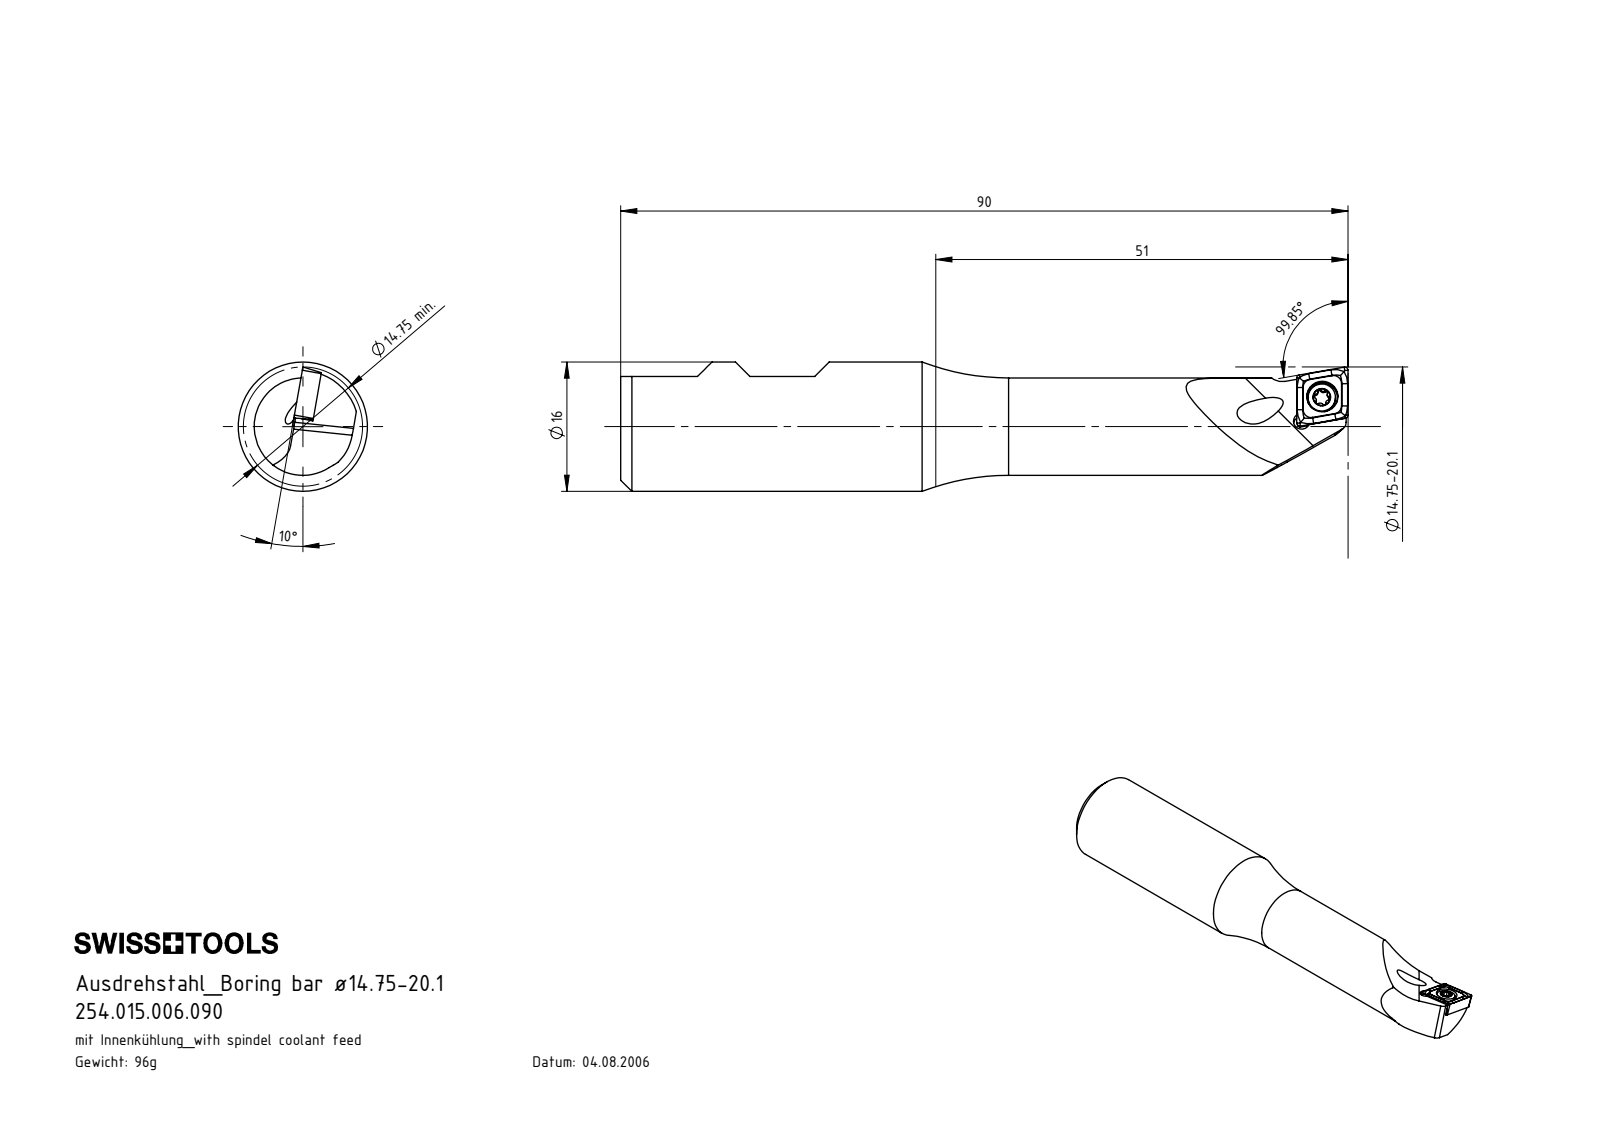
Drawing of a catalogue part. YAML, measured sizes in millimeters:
part_name: "B15-WCA.K11.090_A; WCA-ER2.001.006_A; CCMT060204; B15.WCA.K11.090"
step_written_by: "SolidWorks 2017 (AUTOMOTIVE_DESIGN)"
units: millimeters
bodies: {solids: 3, faces: 126, planar: 33, cylindrical: 39, other: 54}
overall_size: [90, 16, 16]
volume: 12162
surface_area: 4986
round_holes:
  - {diameter: 3, count: 2}
  - {diameter: 2, count: 1}
  - {diameter: 2.05, count: 1}
  - {diameter: 2.8, count: 1}
  - {diameter: 3.85, count: 1}
round_bosses_or_shafts:
  - {diameter: 16, count: 1}
  - {diameter: 12.05, count: 1}
  - {diameter: 3.4, count: 1}
  - {diameter: 2.5, count: 1}
partial_cylinders:
  - {radius: 0.21, count: 6}
  - {radius: 0.36, count: 5}
  - {radius: 0.36, count: 1}
  - {radius: 1, count: 1}
  - {radius: 6.2, count: 1}
  - {radius: 7, count: 1}
  - {radius: 8, count: 1}
face_to_face_distances: [2.18, 10.25, 5.1, 7.28, 7.48, 2.38, 83.76, 1.48, 6.58, 0.7]
hole_center_spacings: [3.89, 3.99]
